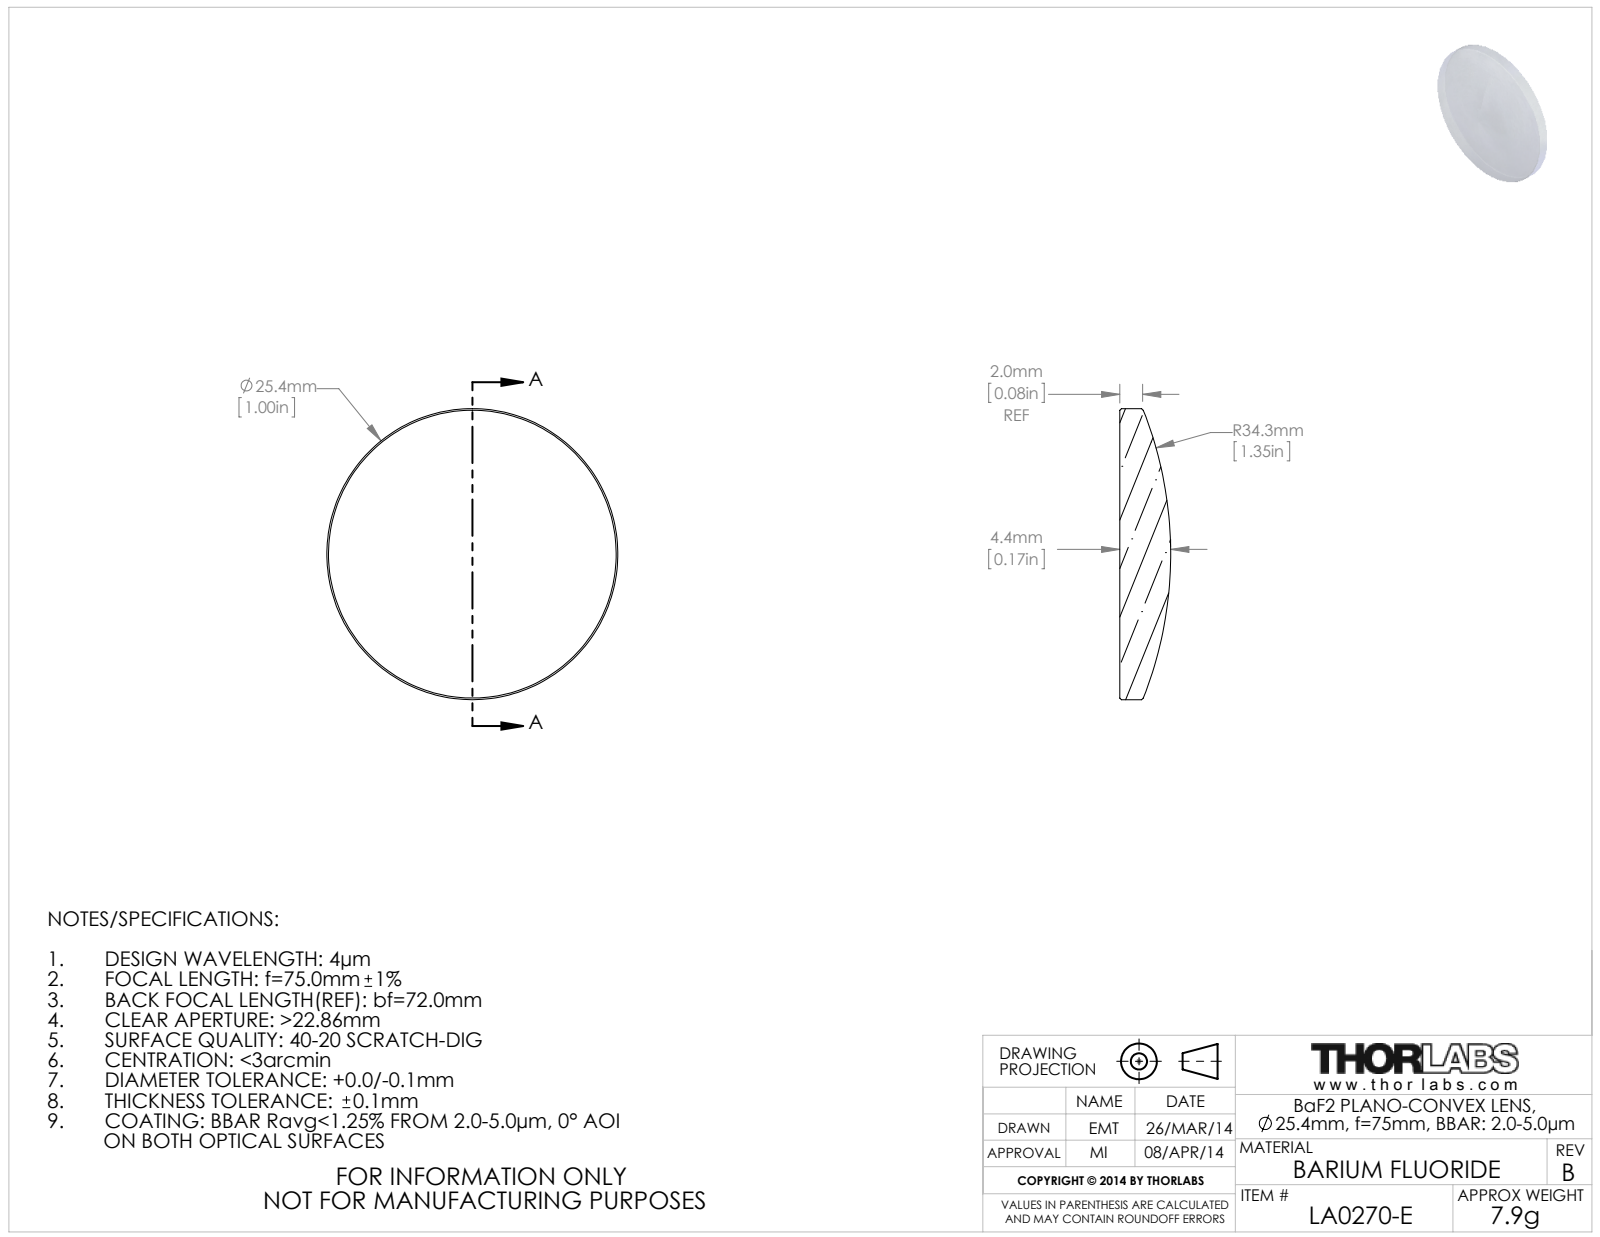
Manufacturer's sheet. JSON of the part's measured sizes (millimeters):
{"part_name": "20094-E0W", "step_written_by": "SolidWorks 2014 (CONFIG_CONTROL_DESIGN)", "units": "millimeters", "bodies": {"solids": 1, "faces": 9, "planar": 1, "cylindrical": 2, "other": 6}, "overall_size": [25.4, 25.4, 4.44], "volume_mm3": 1638, "surface_area_mm2": 1182, "round_bosses_or_shafts": [[25.4, 1]]}
